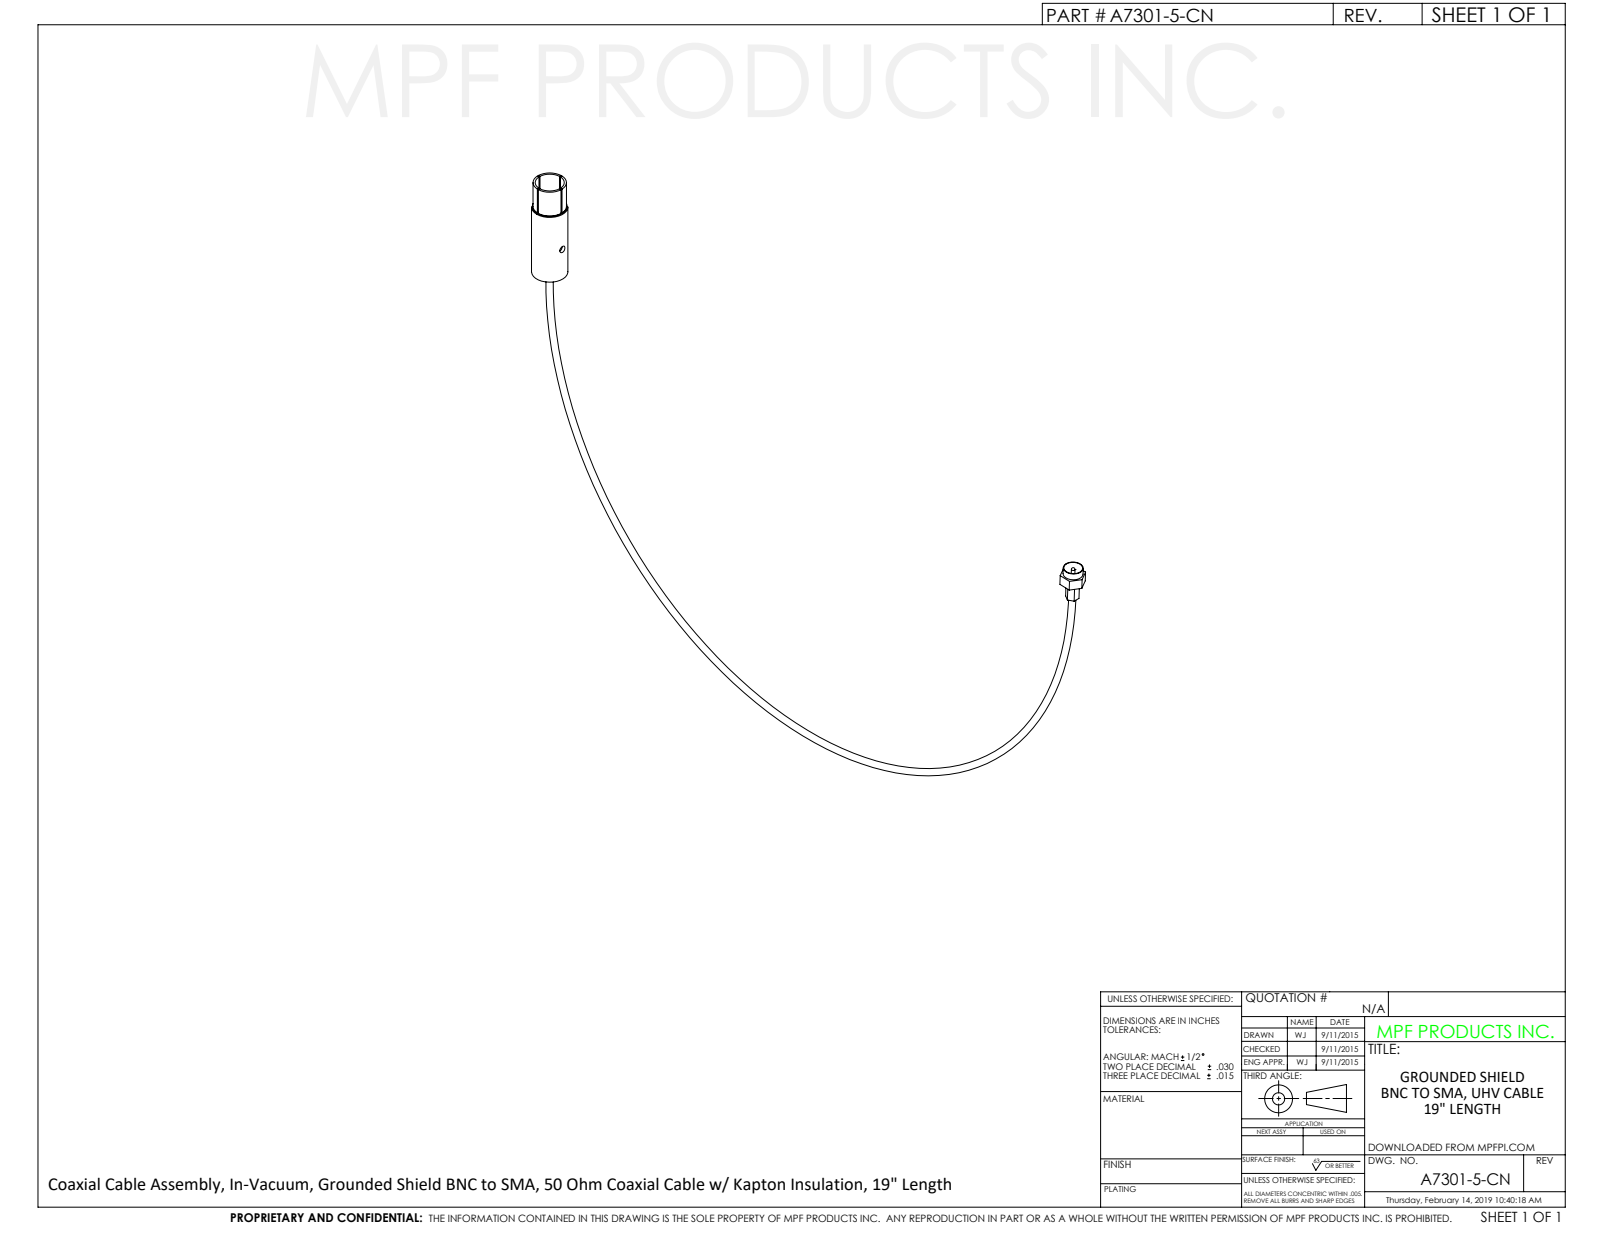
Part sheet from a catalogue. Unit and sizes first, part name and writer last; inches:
Units: inches
Overall size (bounding box): 10.985 × 6.833 × 0.75
Round holes (diameter × count): ⌀0.1 ×2, ⌀0.5 ×1, ⌀0.609 ×1
Round bosses / shafts (diameter × count): ⌀0.75 ×1, ⌀0.71 ×1, ⌀0.669 ×1, ⌀0.1 ×1
Main face-to-face distances: 0.712, 0.3, 0.2, 1.5, 1.3, 0.02, 0.712, 0.1, 0.4, 0.165
Volume: 0.677 in³ · Surface area: 14.62 in²
Bodies: 1 solid, 58 faces (33 planar, 18 cylindrical, 7 other)
Part name (STEP PRODUCT): A7301-5-CN
STEP written by: SolidWorks 2012 (CONFIG_CONTROL_DESIGN)
